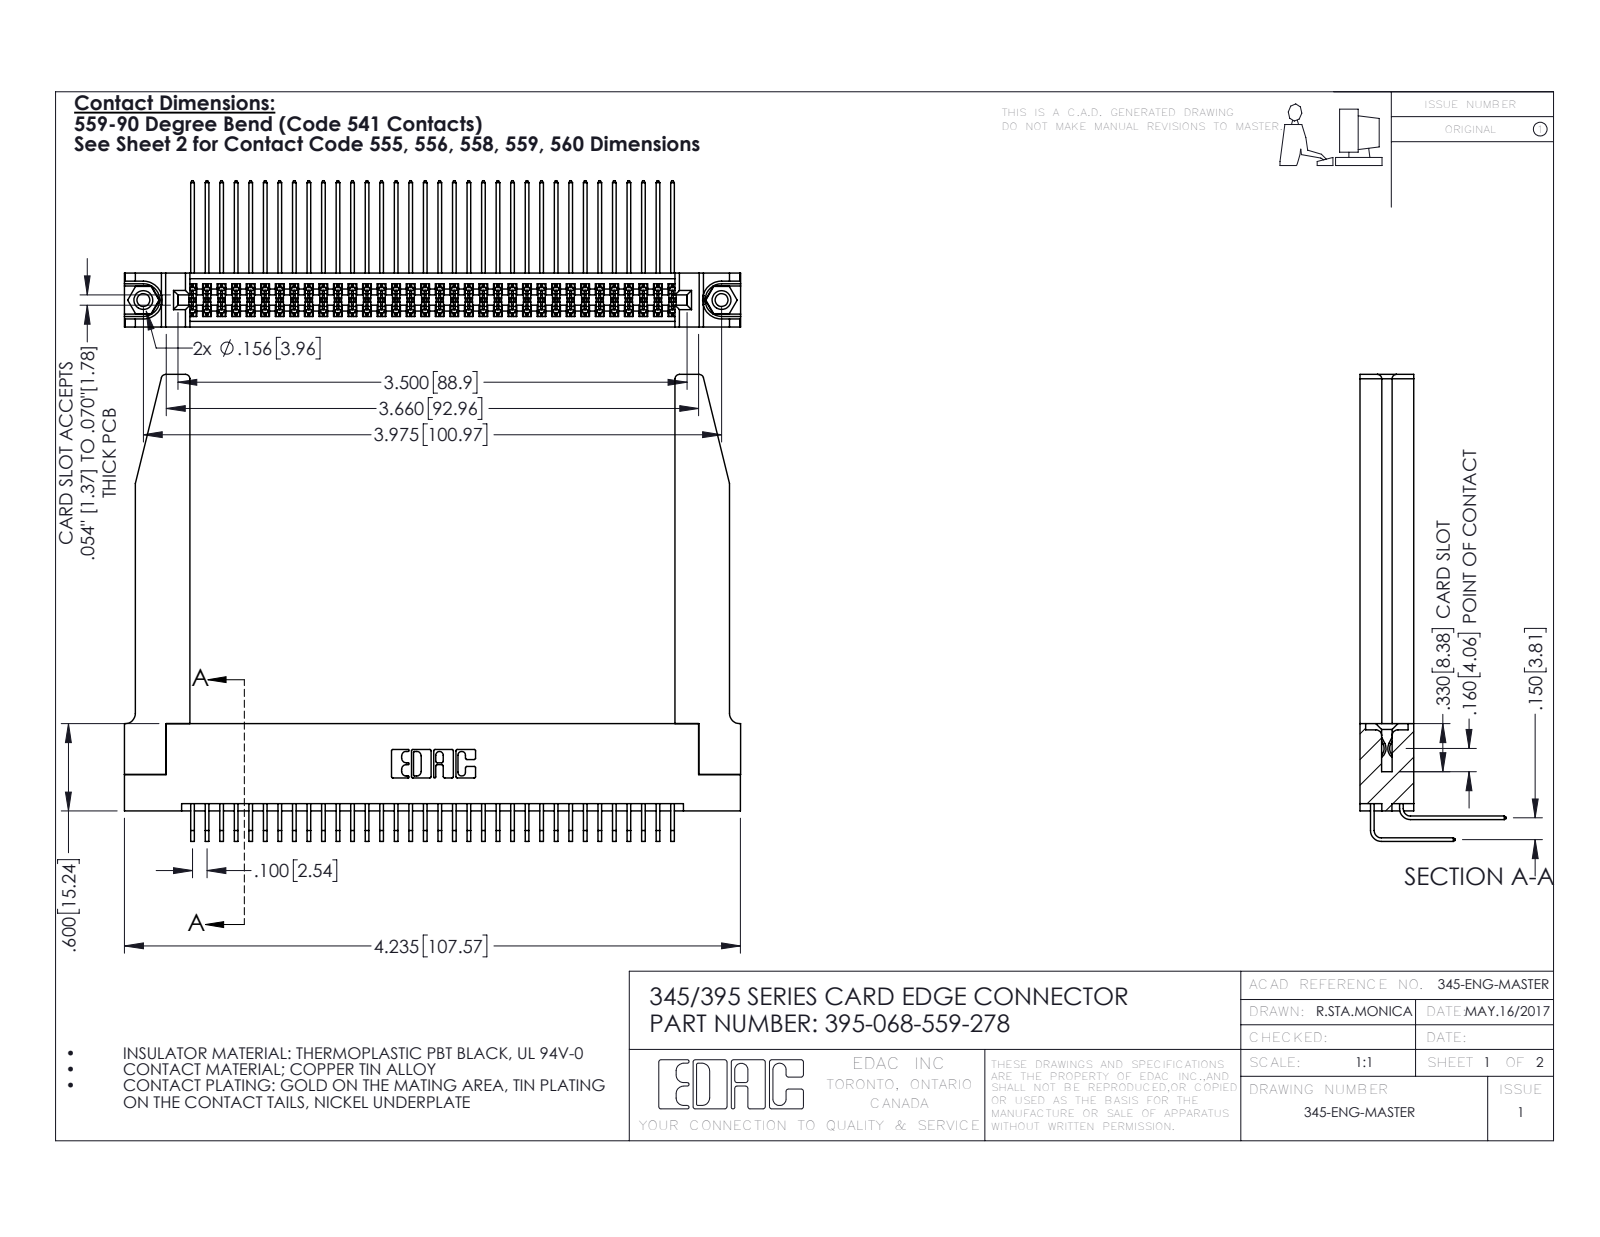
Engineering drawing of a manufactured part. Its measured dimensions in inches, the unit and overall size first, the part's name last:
Units: inches
Overall size (bounding box): 4.236 × 3.209 × 1.005
Round holes (diameter × count): ⌀0.089 ×2, ⌀0.125 ×2, ⌀0.156 ×2, ⌀0.064 ×1
Round bosses / shafts (diameter × count): ⌀0.155 ×2
Partial cylindrical surfaces — rounded edges, fillets, slot ends (radius × count): R0.006 ×103, R0.01 ×22, R0.03 ×8, R0.007 ×6, R0.031 ×6, R0.026 ×3, R0.014 ×2, R0.019 ×2
Main face-to-face distances: 0.37, 0.072, 0.298, 0.2, 0.098, 0.272, 0.025, 0.225, 0.175, 0.15
Hole centre spacings: 0.27, 3.74, 3.975
Volume: 1.131 in³ · Surface area: 37.89 in²
Bodies: 73 solids, 3896 faces (2602 planar, 1242 cylindrical, 52 other)
Part name (STEP PRODUCT): 395-068-559-278; 345-250-001_345-250-001-102; 345-220-078_345-220-078; 345 Part_Flush Mounting Lugs - 0.156 Dia-TH (+2 more)
STEP written by: SolidWorks 2016 (CONFIG_CONTROL_DESIGN)
